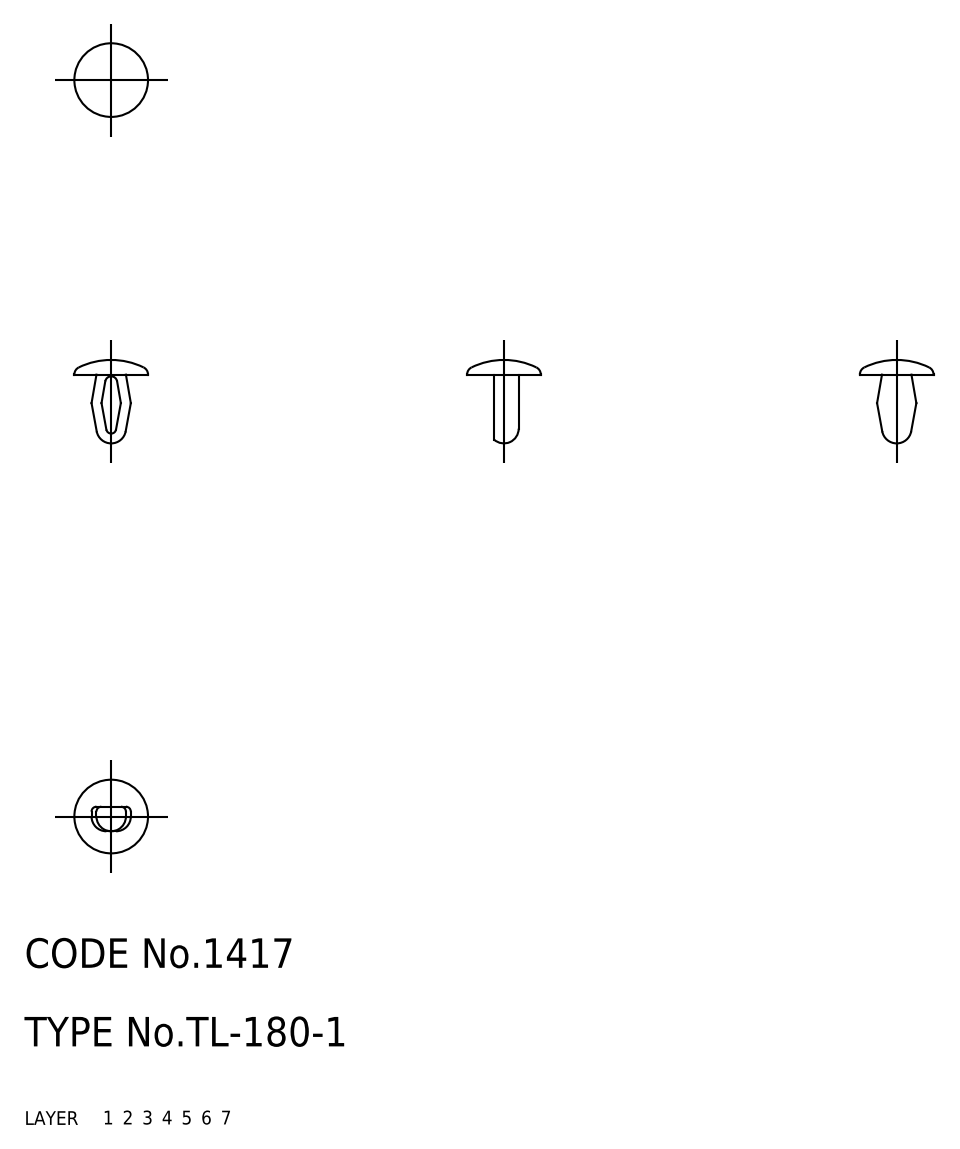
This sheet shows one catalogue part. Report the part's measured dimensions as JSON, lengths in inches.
{"part_name": "fastener", "step_written_by": "CADfix (AUTOMOTIVE_DESIGN)", "units": "inches", "bodies": {"solids": 1, "faces": 26, "planar": 0, "cylindrical": 0, "other": 26}, "overall_size": [0.335, 0.295, 0.295], "volume_in3": 0.005, "surface_area_in2": 0.281}
